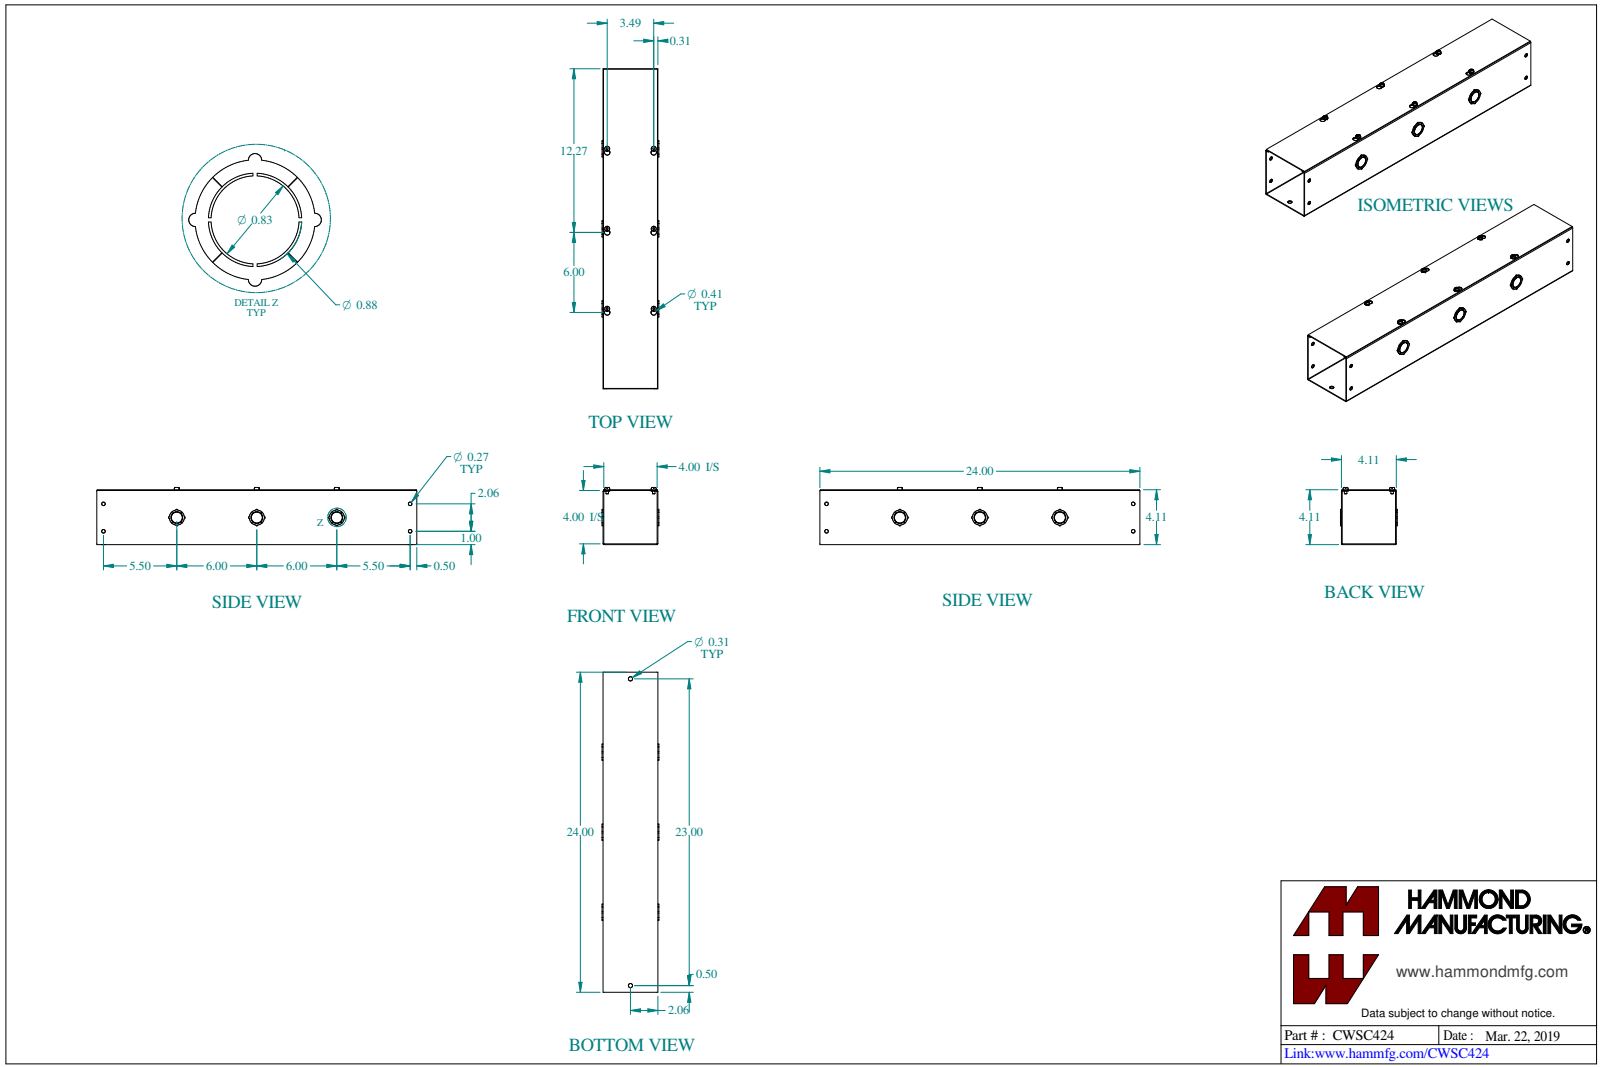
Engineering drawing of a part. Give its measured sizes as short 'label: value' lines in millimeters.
name: CWSC424
written by: SolidWorks 2023 (CONFIG_CONTROL_DESIGN)
unit: mm
bodies: 8 solids, 494 faces (220 planar, 238 cylindrical, 36 other)
size: 609.6 × 108.9 × 108.2
volume: 386 200 mm³; area: 531 700 mm²
holes: 6× ⌀4.5, 4× ⌀6.8, 3× ⌀22.2, 2× ⌀8
bosses: 6× ⌀9.5, 6× ⌀4.8, 3× ⌀28.6, 3× ⌀28.6, 3× ⌀21
rounds: 9× R1.6, 6× R3.2, 6× R5.2, 4× R0.7, 4× R2.2, 3× R1.6
face distances: 1.4, 103, 101.6, 104.5, 100.2, 2.9, 1.8, 3.3, 104.9, 106.3
hole spacings: 152.4, 142.1, 146.6, 176.3, 293.3, 295.4, 445.3, 446.7
